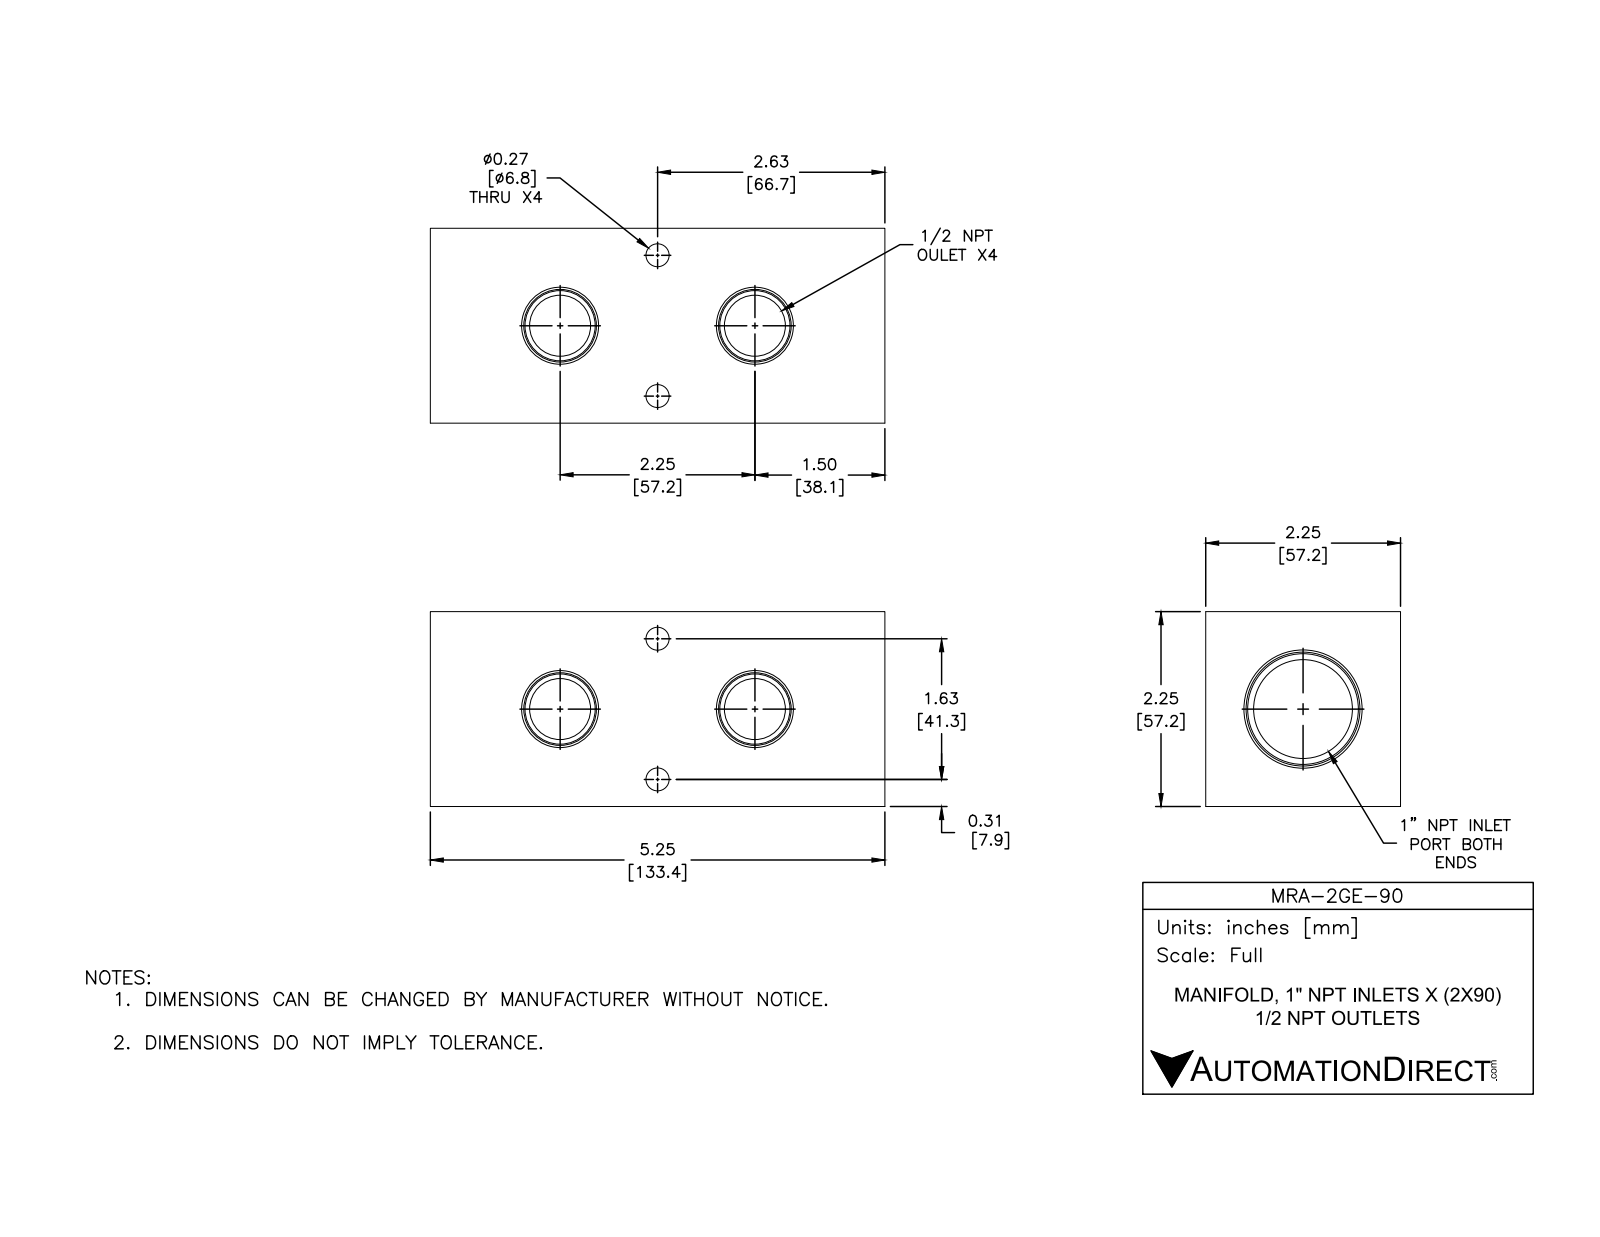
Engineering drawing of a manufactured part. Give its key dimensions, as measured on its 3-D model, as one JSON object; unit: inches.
{"part_name": "MRA-2GE-90", "step_written_by": "SolidWorks 2015 (CONFIG_CONTROL_DESIGN)", "units": "inches", "bodies": {"solids": 1, "faces": 70, "planar": 12, "cylindrical": 34, "other": 24}, "overall_size": [5.25, 2.25, 2.25], "volume_in3": 19.14, "surface_area_in2": 83.2, "round_holes": [[0.266, 4], [0.703, 4], [1.141, 1]], "face_to_face_distances": [2.25, 5.25, 0.66, 4.59, 0.53, 1.72, 3.93], "hole_center_spacings": [1.388, 1.625, 2.25]}
